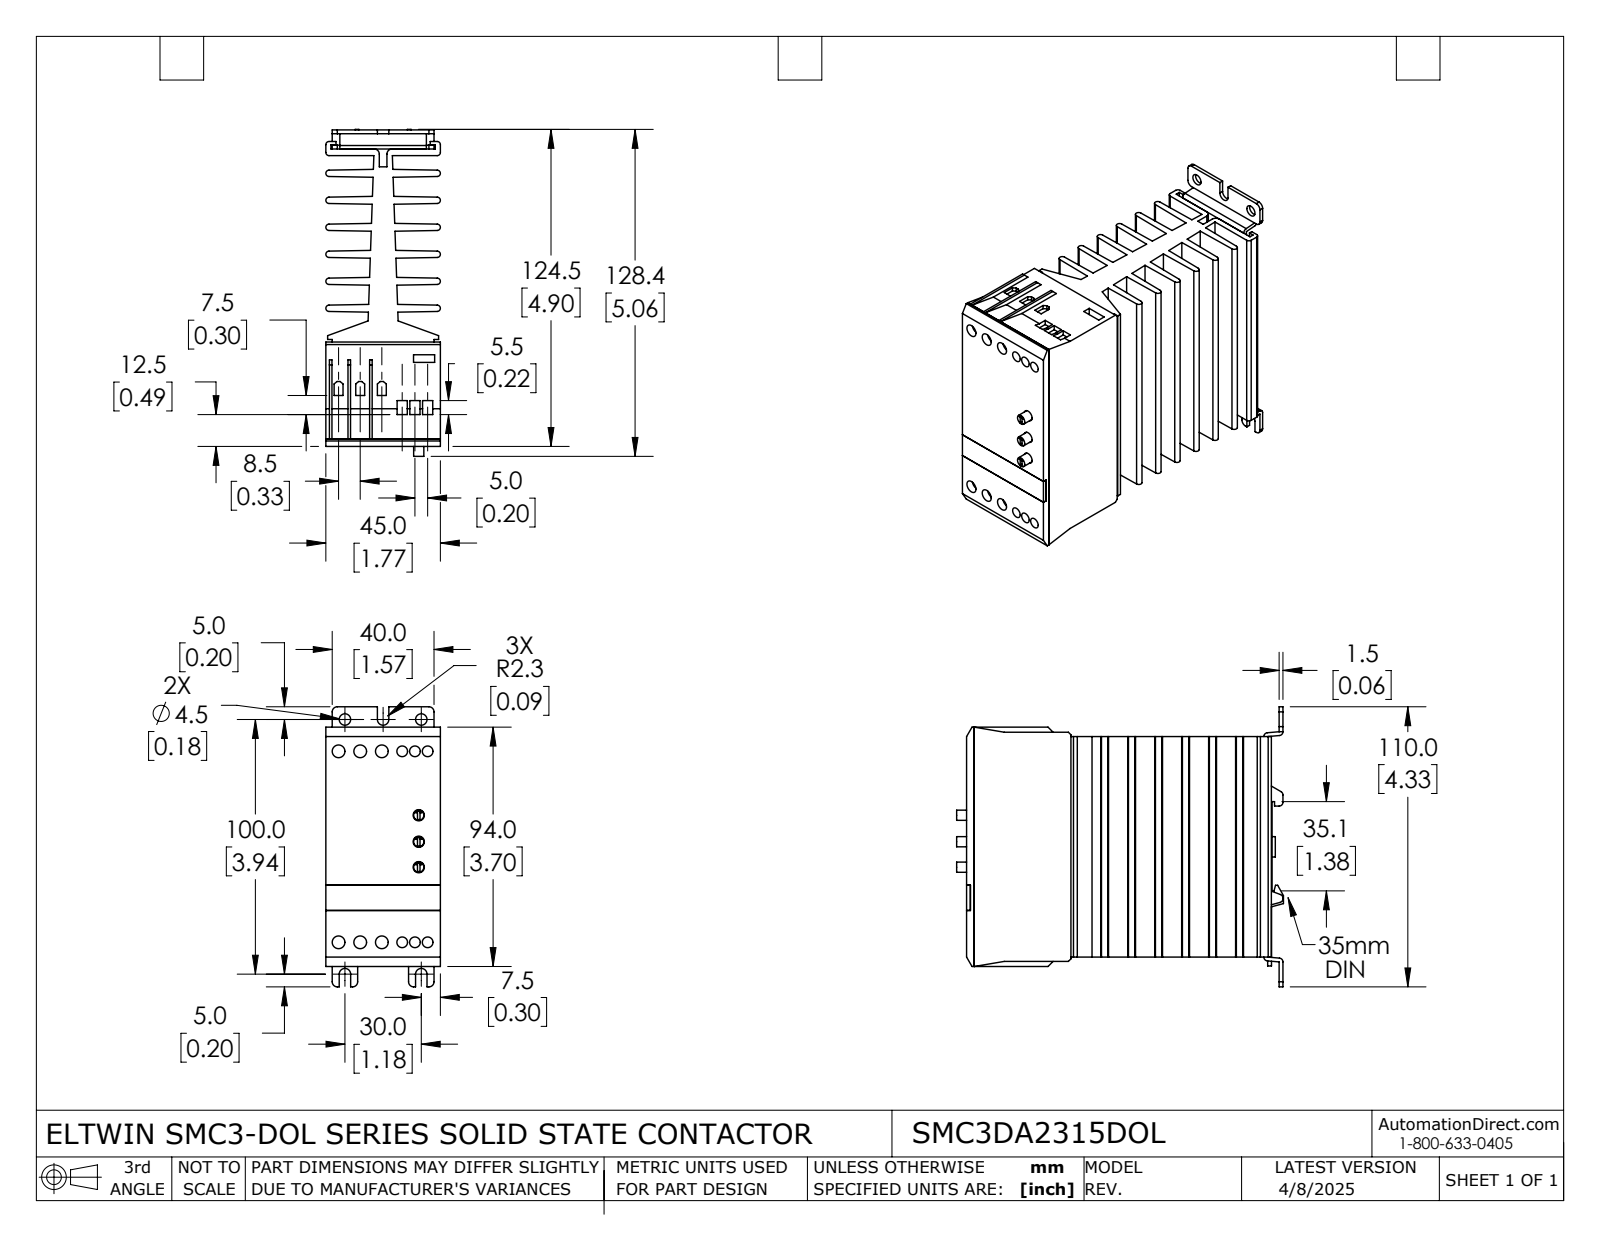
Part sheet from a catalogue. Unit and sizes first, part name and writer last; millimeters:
Units: millimetres
Overall size (bounding box): 128.4 × 110 × 45
Round holes (diameter × count): ⌀4.4 ×9, ⌀4.2 ×6, ⌀5 ×6, ⌀6 ×6, ⌀4.5 ×2
Round bosses / shafts (diameter × count): ⌀4 ×3, ⌀8 ×1
Partial cylindrical surfaces — rounded edges, fillets, slot ends (radius × count): R2 ×18, R1.2 ×16, R1.5 ×10, R1.3 ×4, R2.3 ×3
Main face-to-face distances: 10.6, 21.2, 3.2, 31.8, 7.4, 13.8, 18, 24.4, 42.4, 28.6
Hole centre spacings: 75, 5, 8.5, 75.2, 75.5, 10, 12.8, 30
Volume: 309 400 mm³ · Surface area: 107 400 mm²
Bodies: 8 solids, 473 faces (348 planar, 123 cylindrical, 2 other)
Part name (STEP PRODUCT): SMC3DA2315DOL
STEP written by: SolidWorks 2021 (AUTOMOTIVE_DESIGN)
